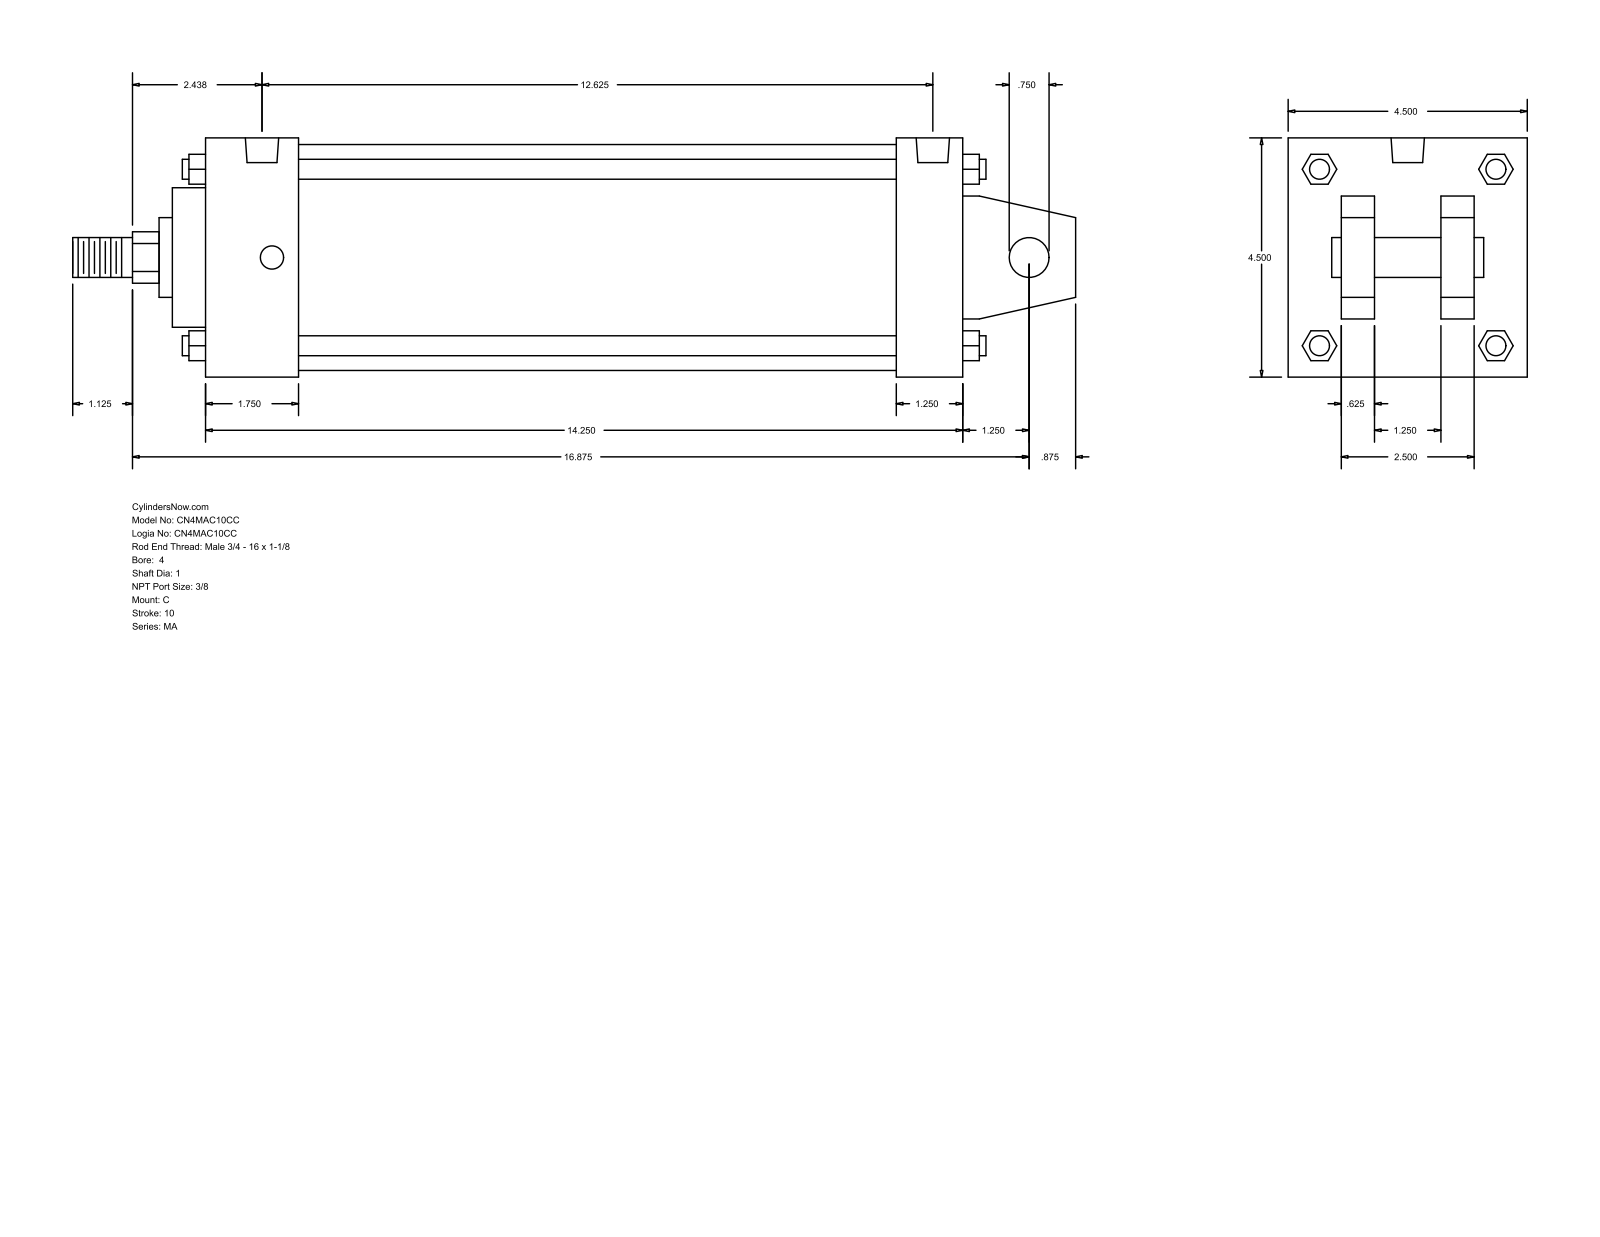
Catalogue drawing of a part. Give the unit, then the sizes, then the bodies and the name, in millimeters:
Units: millimetres
Overall size (bounding box): 479.43 × 114.3 × 114.3
Round holes (diameter × count): ⌀11.11 ×4, ⌀15.93 ×2
Round bosses / shafts (diameter × count): ⌀9.53 ×4, ⌀19.05 ×2, ⌀107.95 ×1, ⌀66.67 ×1, ⌀38.1 ×1, ⌀25.4 ×1
Partial cylindrical surfaces — rounded edges, fillets, slot ends (radius × count): R12.29 ×1
Main face-to-face distances: 114.3, 361.96, 15.87, 31.76, 73.03, 41.27, 25.4, 88.9, 47.63, 330.2
Hole centre spacings: 311.15, 4.76, 4.77, 315.91, 315.92, 320.68
Bodies: 0 solids, 141 faces (109 planar, 32 cylindrical, 0 other)
Part name (STEP PRODUCT): MA_C__0400_1
STEP written by: GSSL Pune (CONFIG_CONTROL_DESIGN)
